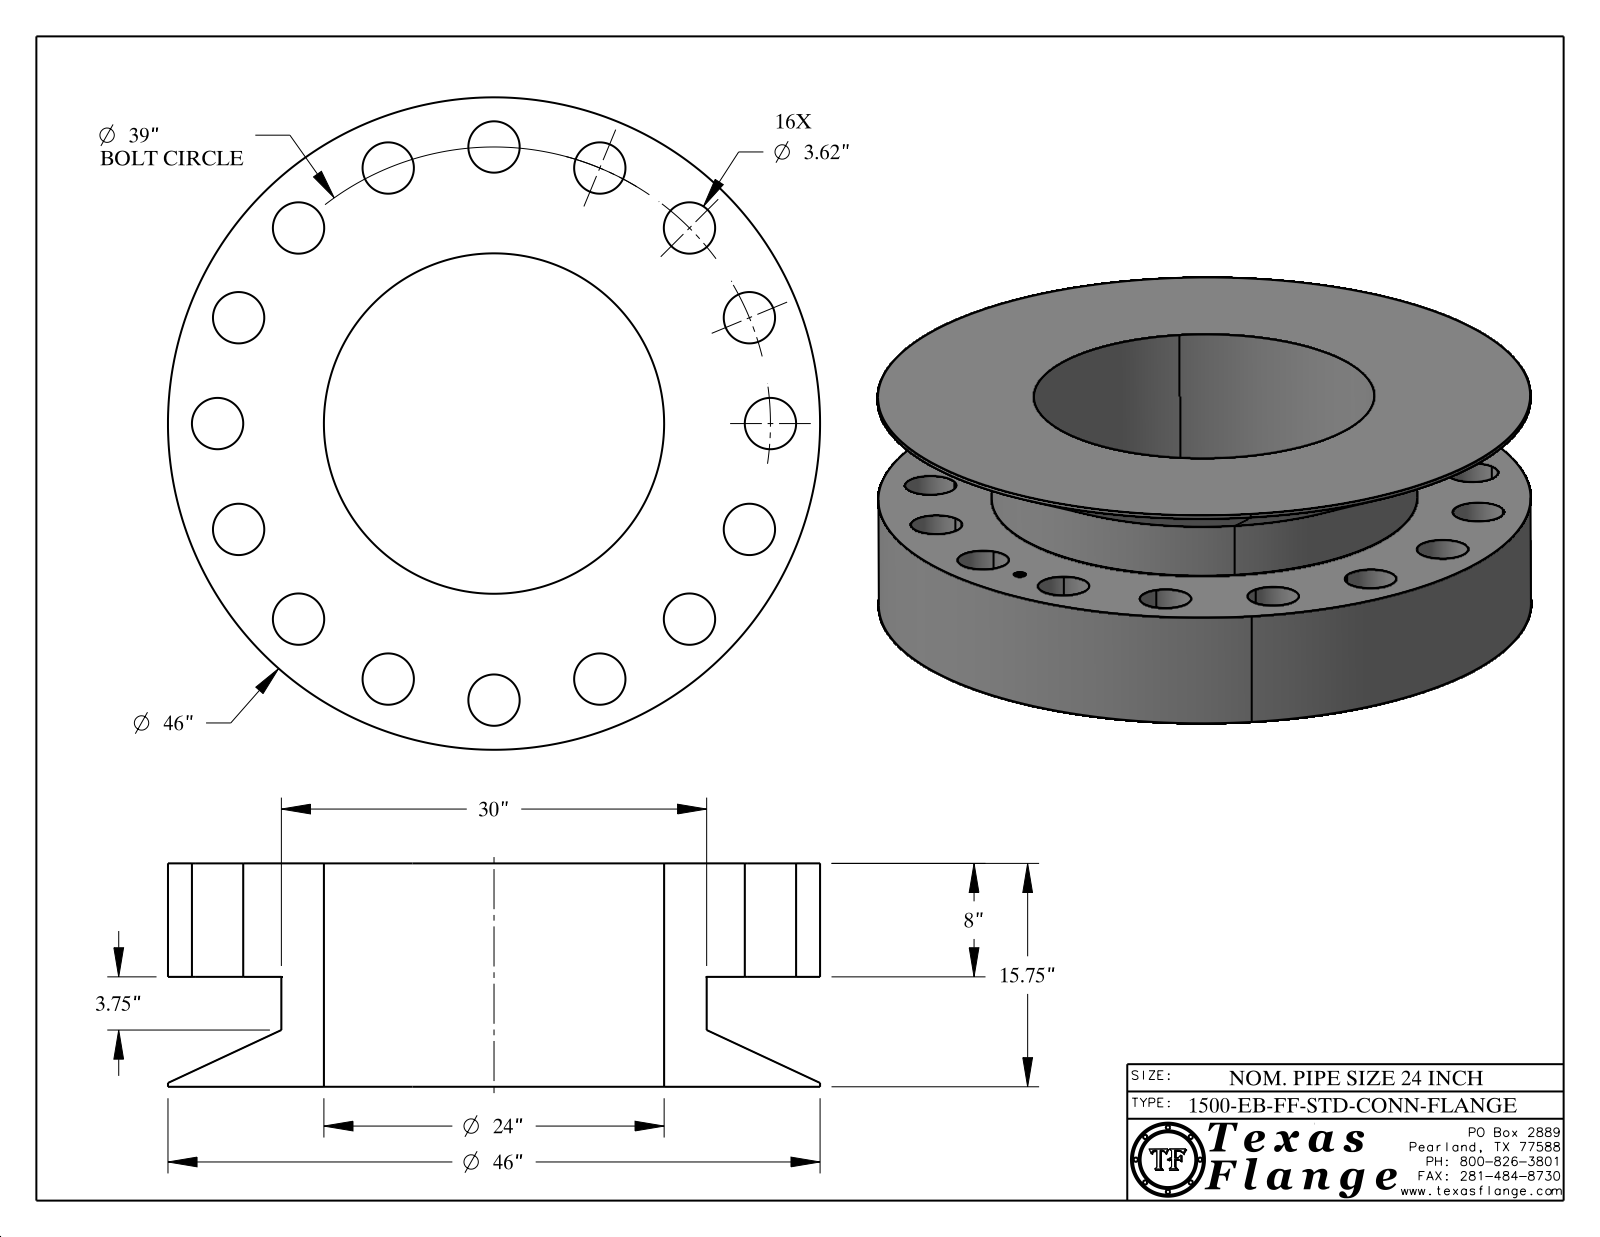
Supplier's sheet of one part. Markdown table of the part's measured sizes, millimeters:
| quantity | value |
| --- | --- |
| part name | 24-1500-EB-FF-STD-CONN-FLANGE |
| STEP written by | CATIA V5 STEP AP214 (AUTOMOTIVE_DESIGN) |
| units | millimeters |
| bodies | 1 solid, 434 faces (368 planar, 60 cylindrical, 6 other) |
| overall size | 1168.4 × 1168.4 × 400.1 |
| volume | 200 700 000 mm³ |
| surface area | 5 351 000 mm² |
| round holes (diameter × count) | 91.9 × 16, 21.6 × 1, 609.6 × 1 |
| round bosses / shafts (diameter × count) | 1.3 × 8, 1168.4 × 1, 762 × 1, 17 × 1 |
| main face-to-face distances | 400.1, 203.2, 196.9, 203.1, 197, 6.5, 6.3, 1.2, 4.2, 5.4 |
| hole center spacings | 495.3, 550.3, 700.5, 971.6, 379.1, 915.2, 193.2, 193.3 |
